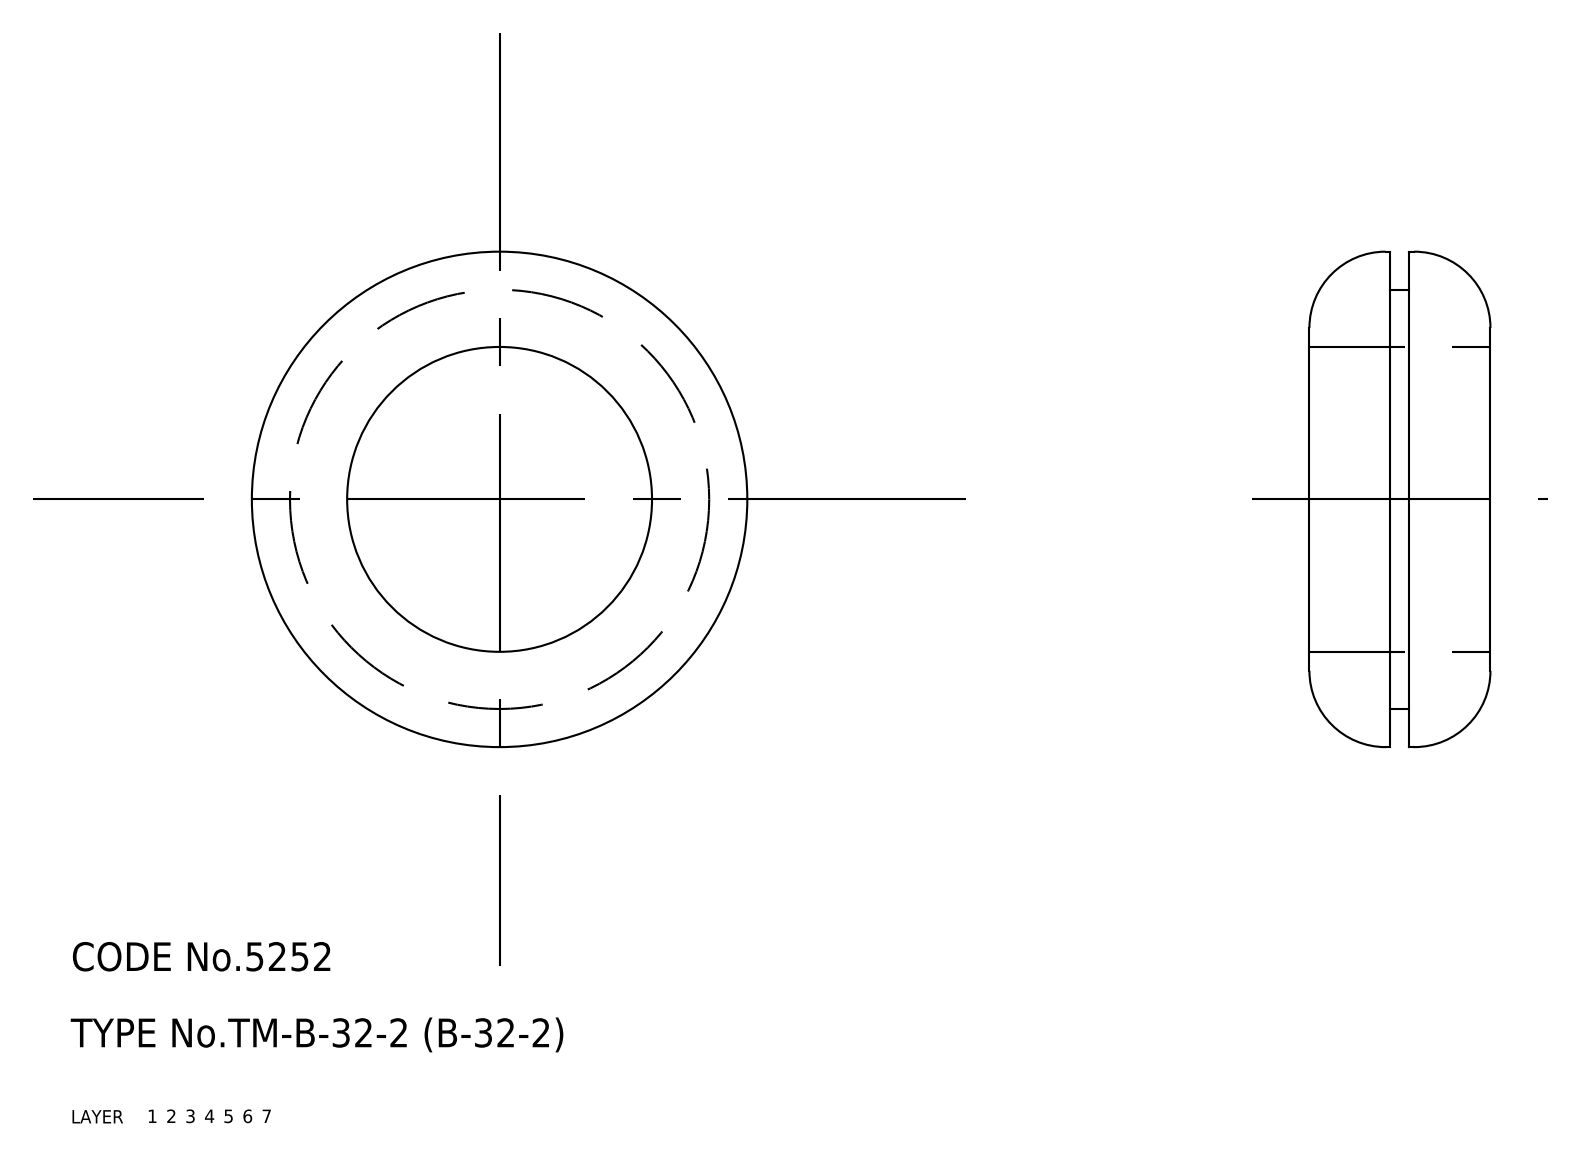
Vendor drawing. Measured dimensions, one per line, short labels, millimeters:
name: grommet
written by: CADfix (AUTOMOTIVE_DESIGN)
unit: mm
bodies: 1 solid, 16 faces (0 planar, 0 cylindrical, 16 other)
size: 52 × 52 × 19
volume: 19 739 mm³; area: 7 635 mm²
